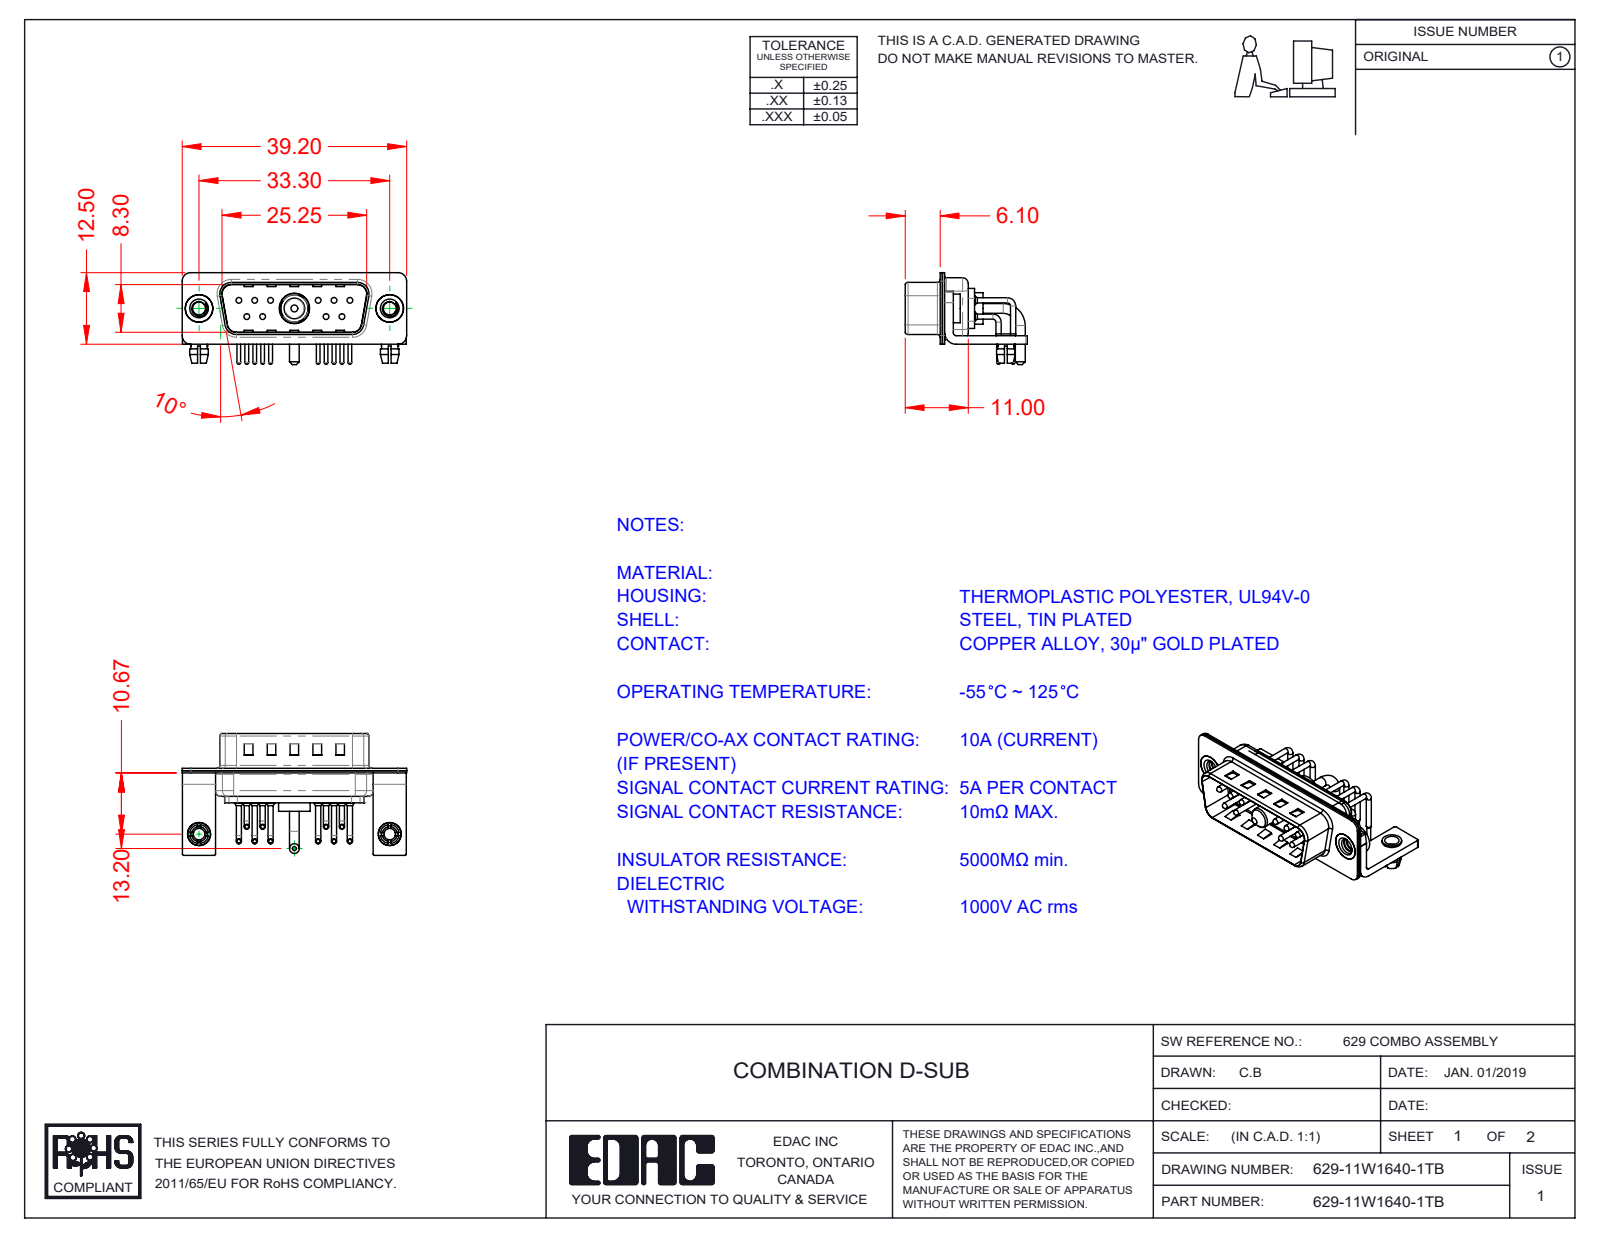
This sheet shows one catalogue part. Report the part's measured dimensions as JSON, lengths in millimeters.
{"part_name": "629Combo Contact Row 1; 629-11W1640-1TB; 629Combo Shell Rear_15 Contacts; 629Combo Threaded Rivet_2 (+6 more)", "step_written_by": "SolidWorks 2020 (CONFIG_CONTROL_DESIGN)", "units": "millimeters", "bodies": {"solids": 21, "faces": 1636, "planar": 866, "cylindrical": 574, "other": 196}, "overall_size": [39.2, 21.3, 16.05], "volume_mm3": 2353, "surface_area_mm2": 6035, "round_holes": [[2, 12], [0.75, 10], [1.6, 10], [2.26, 2], [2.5, 2], [3.2, 2], [4, 2], [4.8, 2], [4.85, 1], [5.3, 1]], "round_bosses_or_shafts": [[0.9, 20], [1.5, 10], [1, 10], [0.65, 10], [5, 2], [4.9, 2], [4, 2], [3.4, 2]], "partial_cylinders_radius": [[0.25, 16], [1.5, 16], [2, 13], [1.01, 10], [0.5, 9], [1.6, 8], [1, 7], [0.6, 4]], "face_to_face_distances": [0.4, 0.8, 1.5, 9.5, 9.1, 0.6, 8.7, 9.9, 1.2, 5.2], "hole_center_spacings": [3.16, 2.77, 13.85, 11.08, 16.62, 5.03, 5.04, 5.54]}
